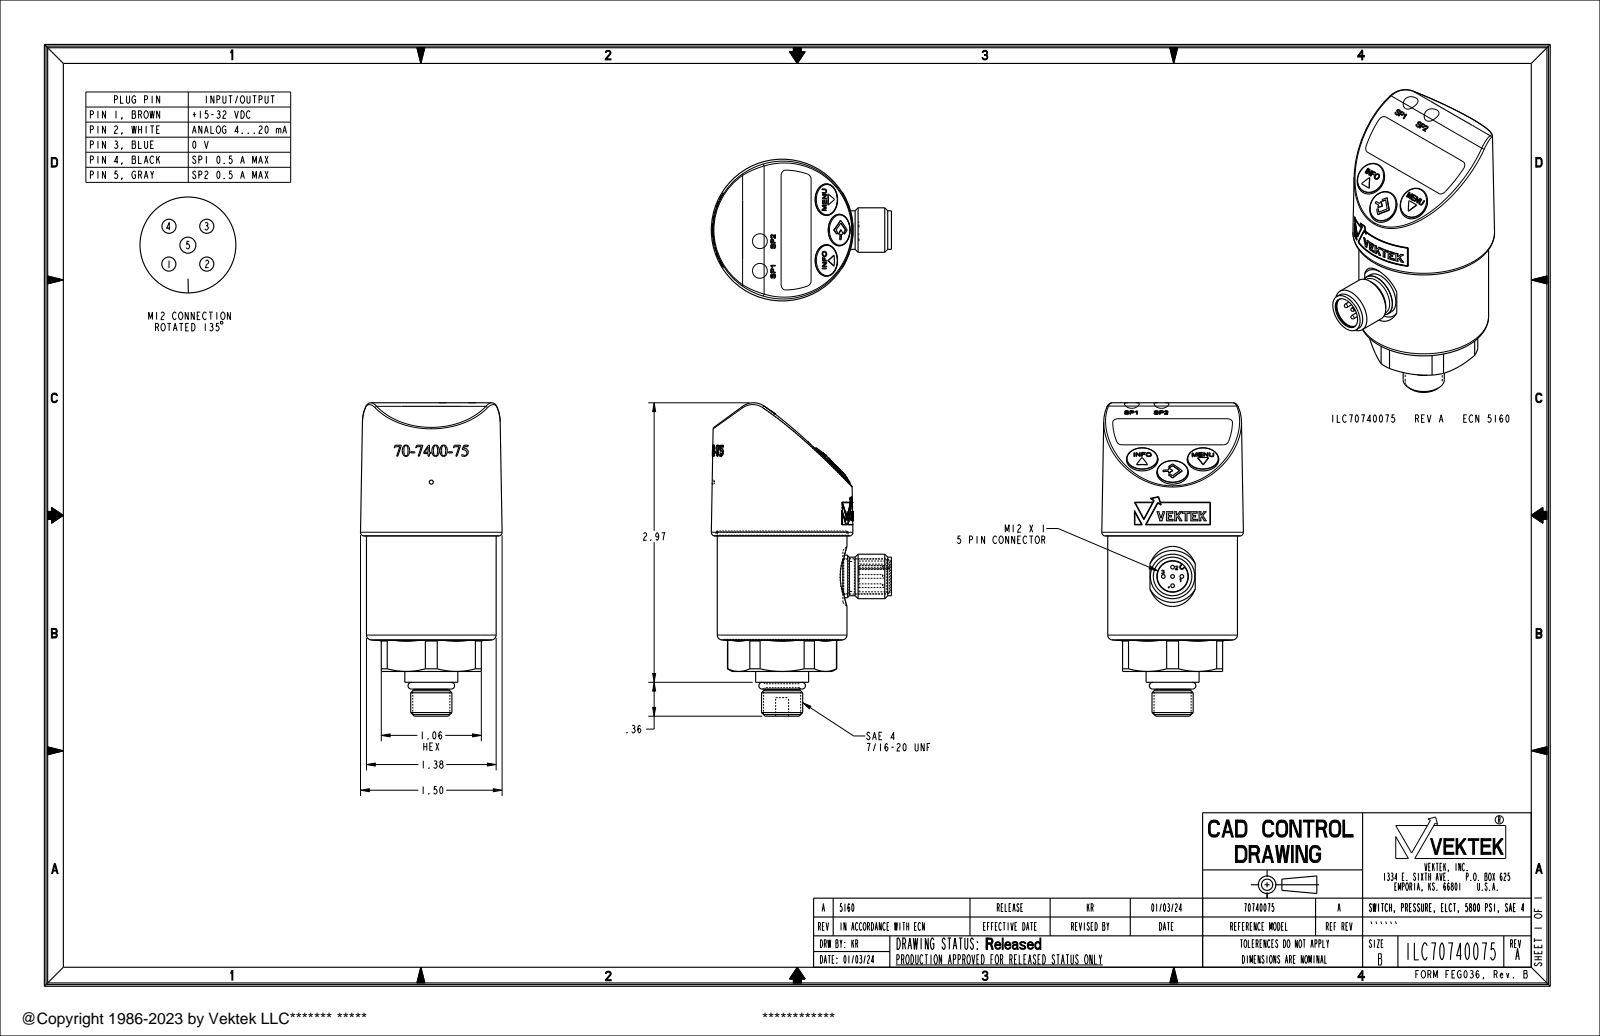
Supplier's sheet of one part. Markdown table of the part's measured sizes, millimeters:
| quantity | value |
| --- | --- |
| part name | ILC70740075 |
| STEP written by | CREO PARAMETRIC BY PTC INC, 2021164 (AUTOMOTIVE_DESIGN) |
| units | millimeters |
| bodies | 9 solids, 795 faces (329 planar, 95 cylindrical, 371 other) |
| overall size | 84.5 × 48.6 × 38.2 |
| volume | 66 840 mm³ |
| surface area | 12 280 mm² |
| round holes (diameter × count) | 1.1 × 1, 3.5 × 1, 8.3 × 1, 8.5 × 1, 9.5 × 1, 31.4 × 1, 35.4 × 1 |
| round bosses / shafts (diameter × count) | 1 × 5, 35 × 1, 30.2 × 1, 14.3 × 1, 12 × 1, 11.5 × 1, 11.1 × 1, 10.4 × 1 |
| partial cylindrical surfaces (radius × count) | 0.1 × 6, 0.2 × 2, 0.6 × 1, 5 × 1, 11.2 × 1, 14.8 × 1, 16.4 × 1, 19.1 × 1 |
| main face-to-face distances | 27, 2.9, 11.3, 8.4, 11.6, 8.7, 9.1, 12.1, 20.5, 20.7 |
| hole center spacings | 25.4 |
